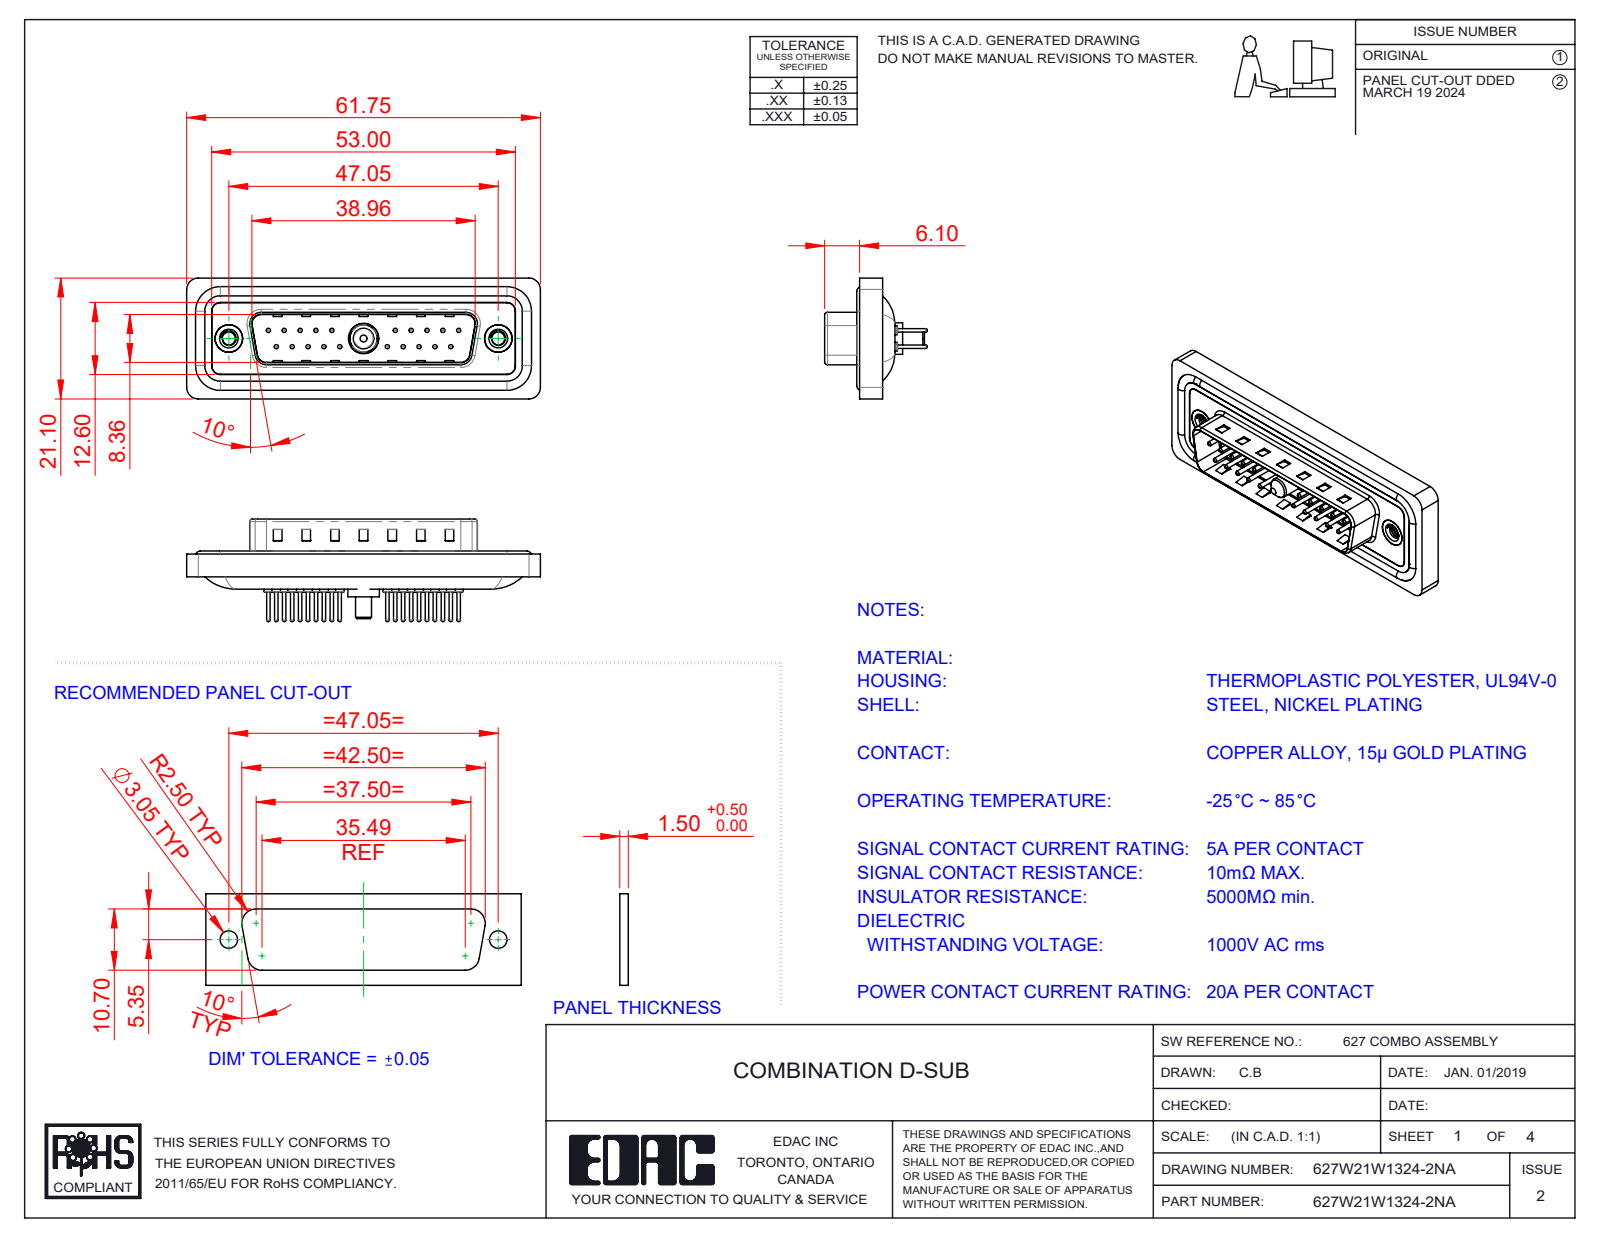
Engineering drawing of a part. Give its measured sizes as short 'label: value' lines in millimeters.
name: 627W21W1324-2NA; 627Combo Threaded Rivet_A; 627Combo Contact Row 2_24; Power Pin_20A S (+5 more)
written by: SolidWorks 2023 (CONFIG_CONTROL_DESIGN)
unit: mm
bodies: 29 solids, 1260 faces (359 planar, 489 cylindrical, 412 other)
size: 61.75 × 21.1 × 17.9
volume: 7 199 mm³; area: 11 951 mm²
holes: 20× ⌀0.75, 20× ⌀1.6, 20× ⌀2, 2× ⌀2.26, 2× ⌀4, 2× ⌀4.8, 2× ⌀5, 1× ⌀4.85, 1× ⌀5.3
bosses: 20× ⌀1.5, 20× ⌀0.6, 4× ⌀1.6, 2× ⌀4.9, 1× ⌀5.5, 1× ⌀5.2, 1× ⌀4.75, 1× ⌀3.75
rounds: 22× R1.5, 18× R2, 8× R0.5, 8× R1.6, 4× R0.25, 4× R0.6, 4× R0.65, 4× R0.9
face distances: 0.4, 1.5, 1.1, 1.6, 0.5, 3.1, 2.9, 4.1, 0.82, 9.58
hole spacings: 3.16, 2.77, 5.54, 8.31, 5.04, 19.39, 20.97, 22.16
